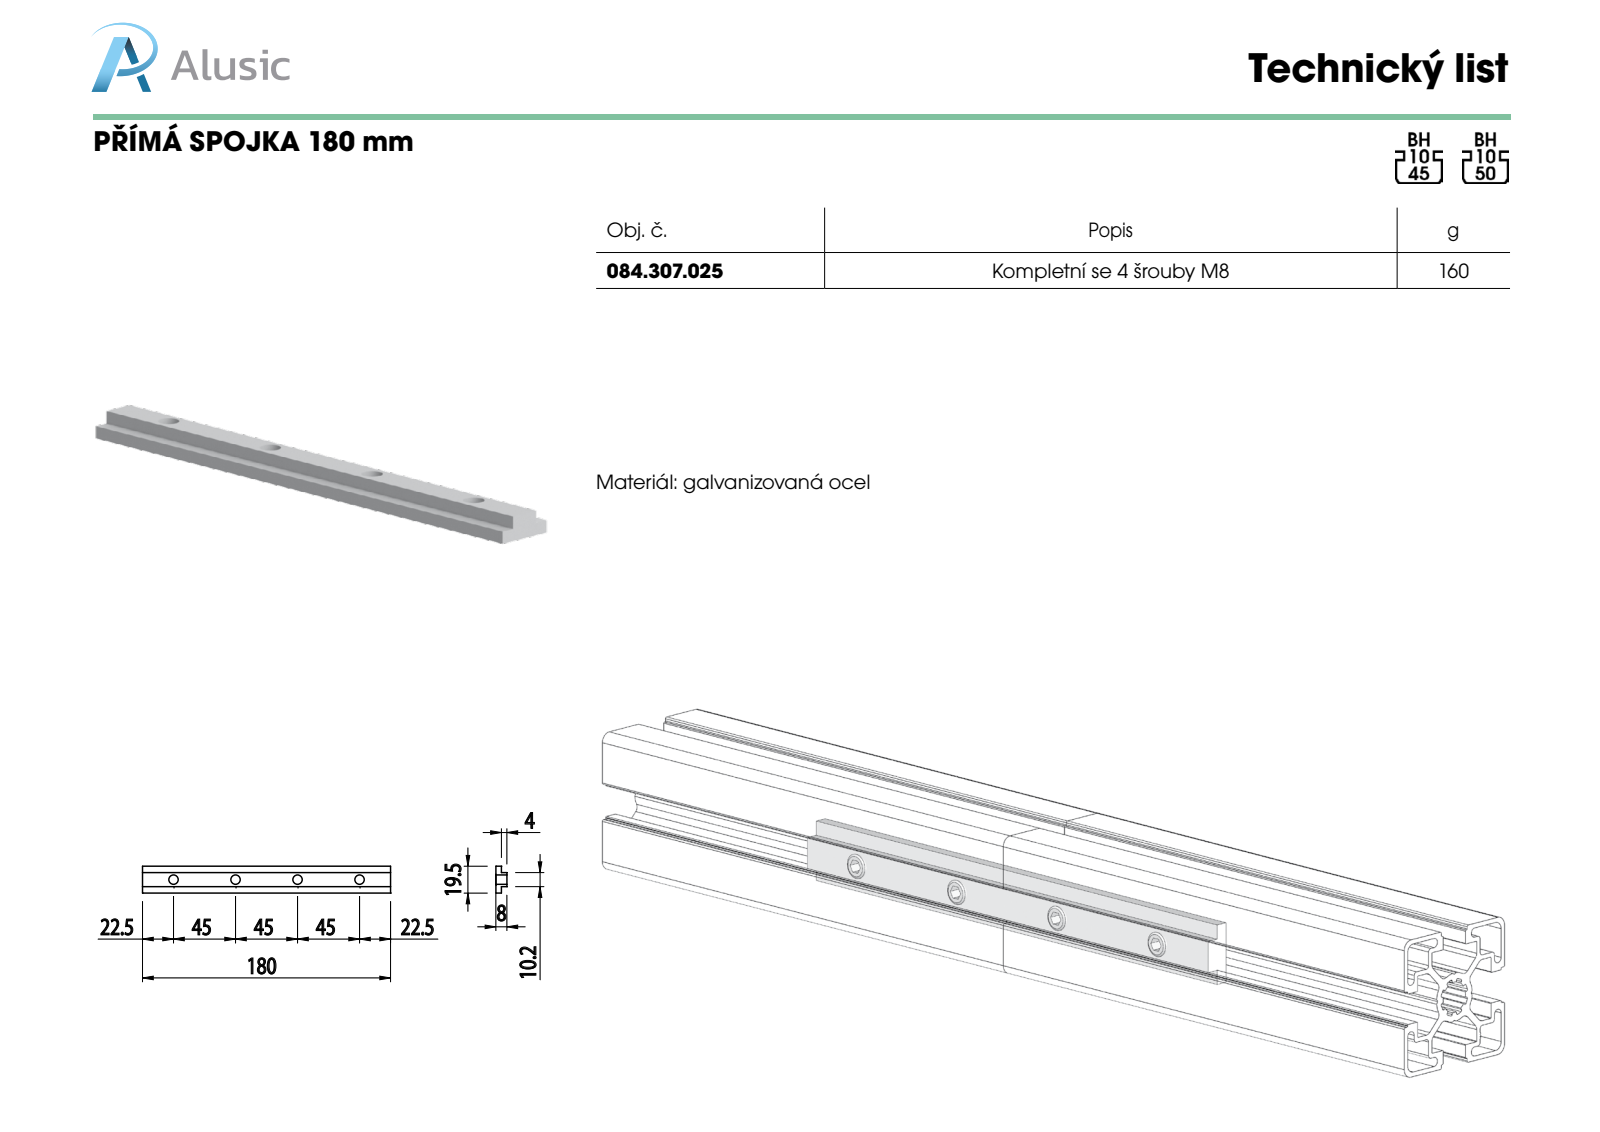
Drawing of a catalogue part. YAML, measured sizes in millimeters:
part_name: "084.307.025"
step_written_by: "SolidWorks 2011 (CONFIG_CONTROL_DESIGN)"
units: millimeters
bodies: {solids: 1, faces: 18, planar: 10, cylindrical: 8, other: 0}
overall_size: [180, 19.5, 8]
volume: 20222
surface_area: 10531
round_holes:
  - {diameter: 6.8, count: 4}
face_to_face_distances: [4, 8, 4.65, 14.85, 19.5, 10.2, 180]
hole_center_spacings: [45, 90, 135]
